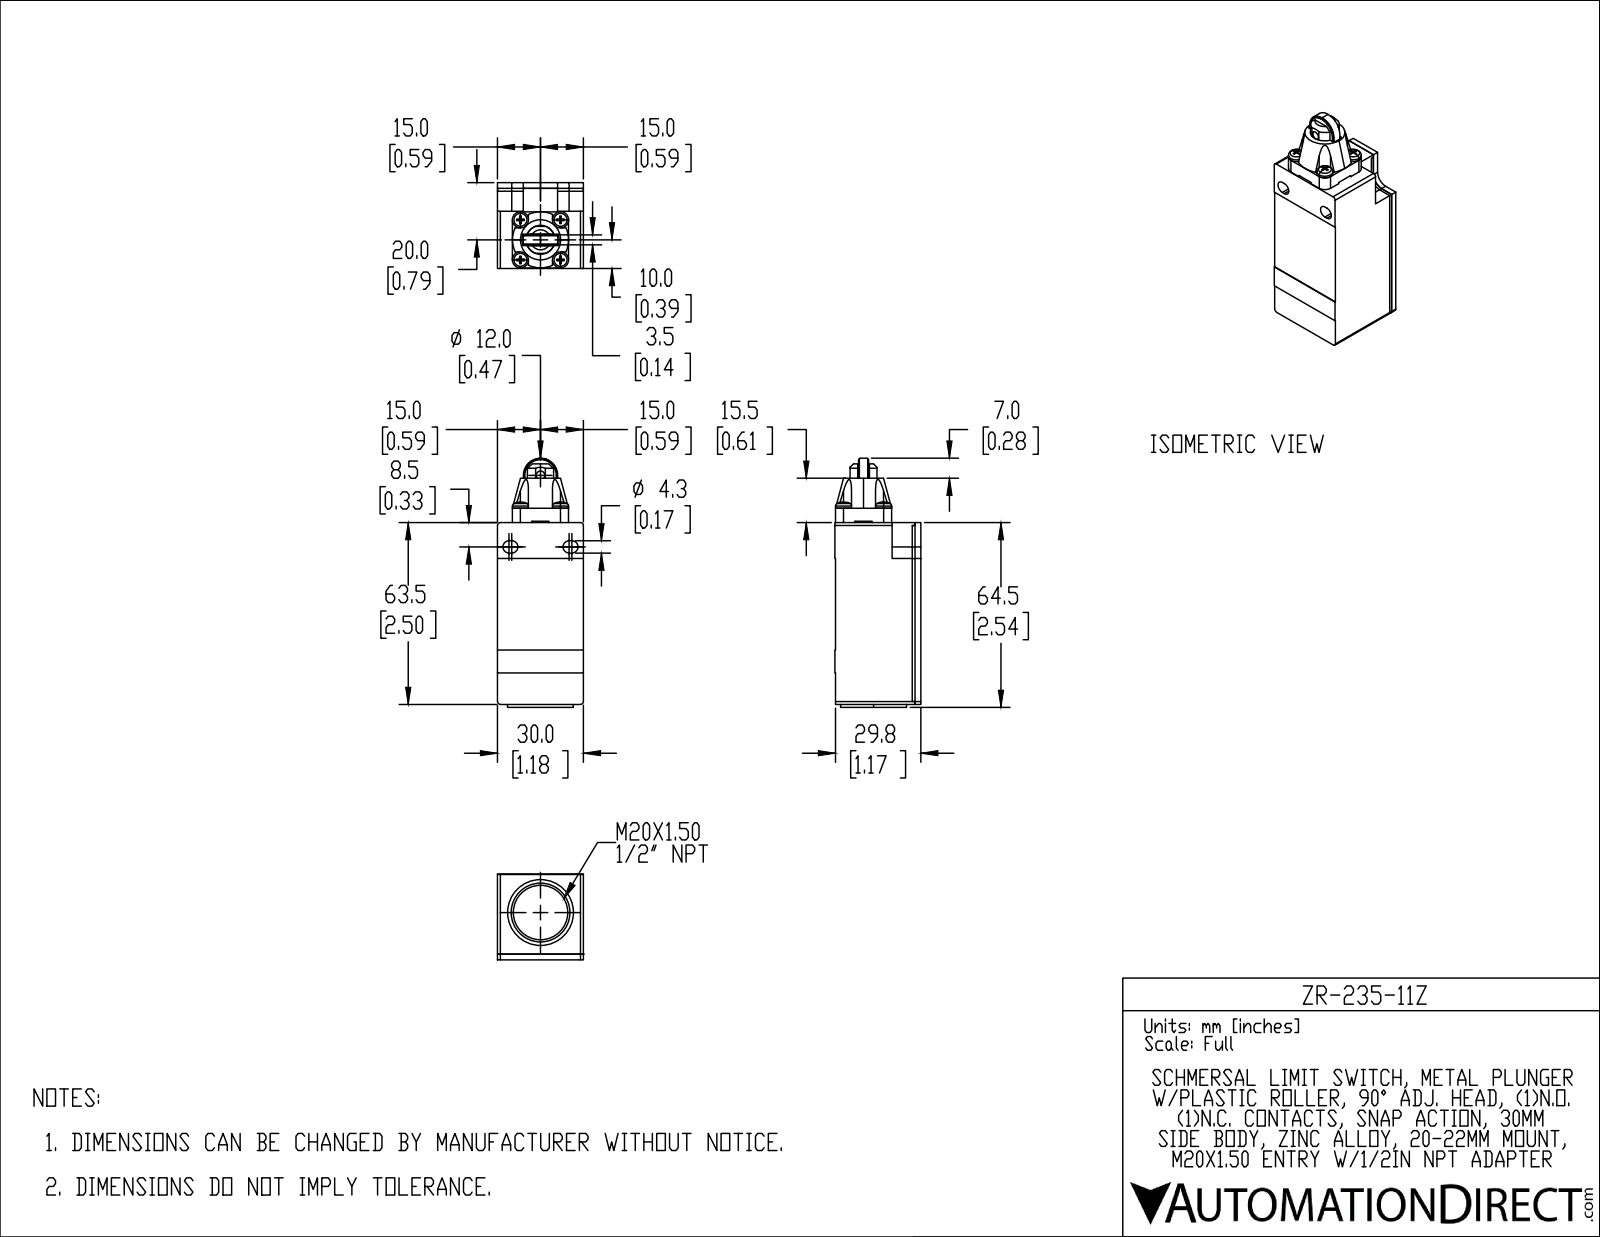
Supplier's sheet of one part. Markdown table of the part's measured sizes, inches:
| quantity | value |
| --- | --- |
| part name | ZR-235-11Z |
| STEP written by | SolidWorks 2019 (AUTOMOTIVE_DESIGN) |
| units | inches |
| bodies | 1 solid, 382 faces (257 planar, 99 cylindrical, 26 other) |
| overall size | 3.425 × 1.181 × 1.181 |
| volume | 3.422 in³ |
| surface area | 21.32 in² |
| round holes (diameter × count) | 0.276 × 3, 0.118 × 1, 0.512 × 1, 0.545 × 1, 0.748 × 1 |
| round bosses / shafts (diameter × count) | 0.213 × 4, 0.256 × 3, 0.221 × 2, 0.906 × 1, 0.472 × 1, 0.415 × 1, 0.276 × 1 |
| partial cylindrical surfaces (radius × count) | 0.02 × 12, 0.11 × 8, 0.039 × 4, 0.085 × 4, 0.11 × 2, 0.157 × 2, 0.159 × 2, 0.197 × 1 |
| main face-to-face distances | 1.181, 1.173, 2.5, 0.207, 2.293, 0.15, 0.78, 0.354, 0.787, 0.394 |
| hole center spacings | 2.228, 3.023, 0.138, 0.807, 0.866 |
